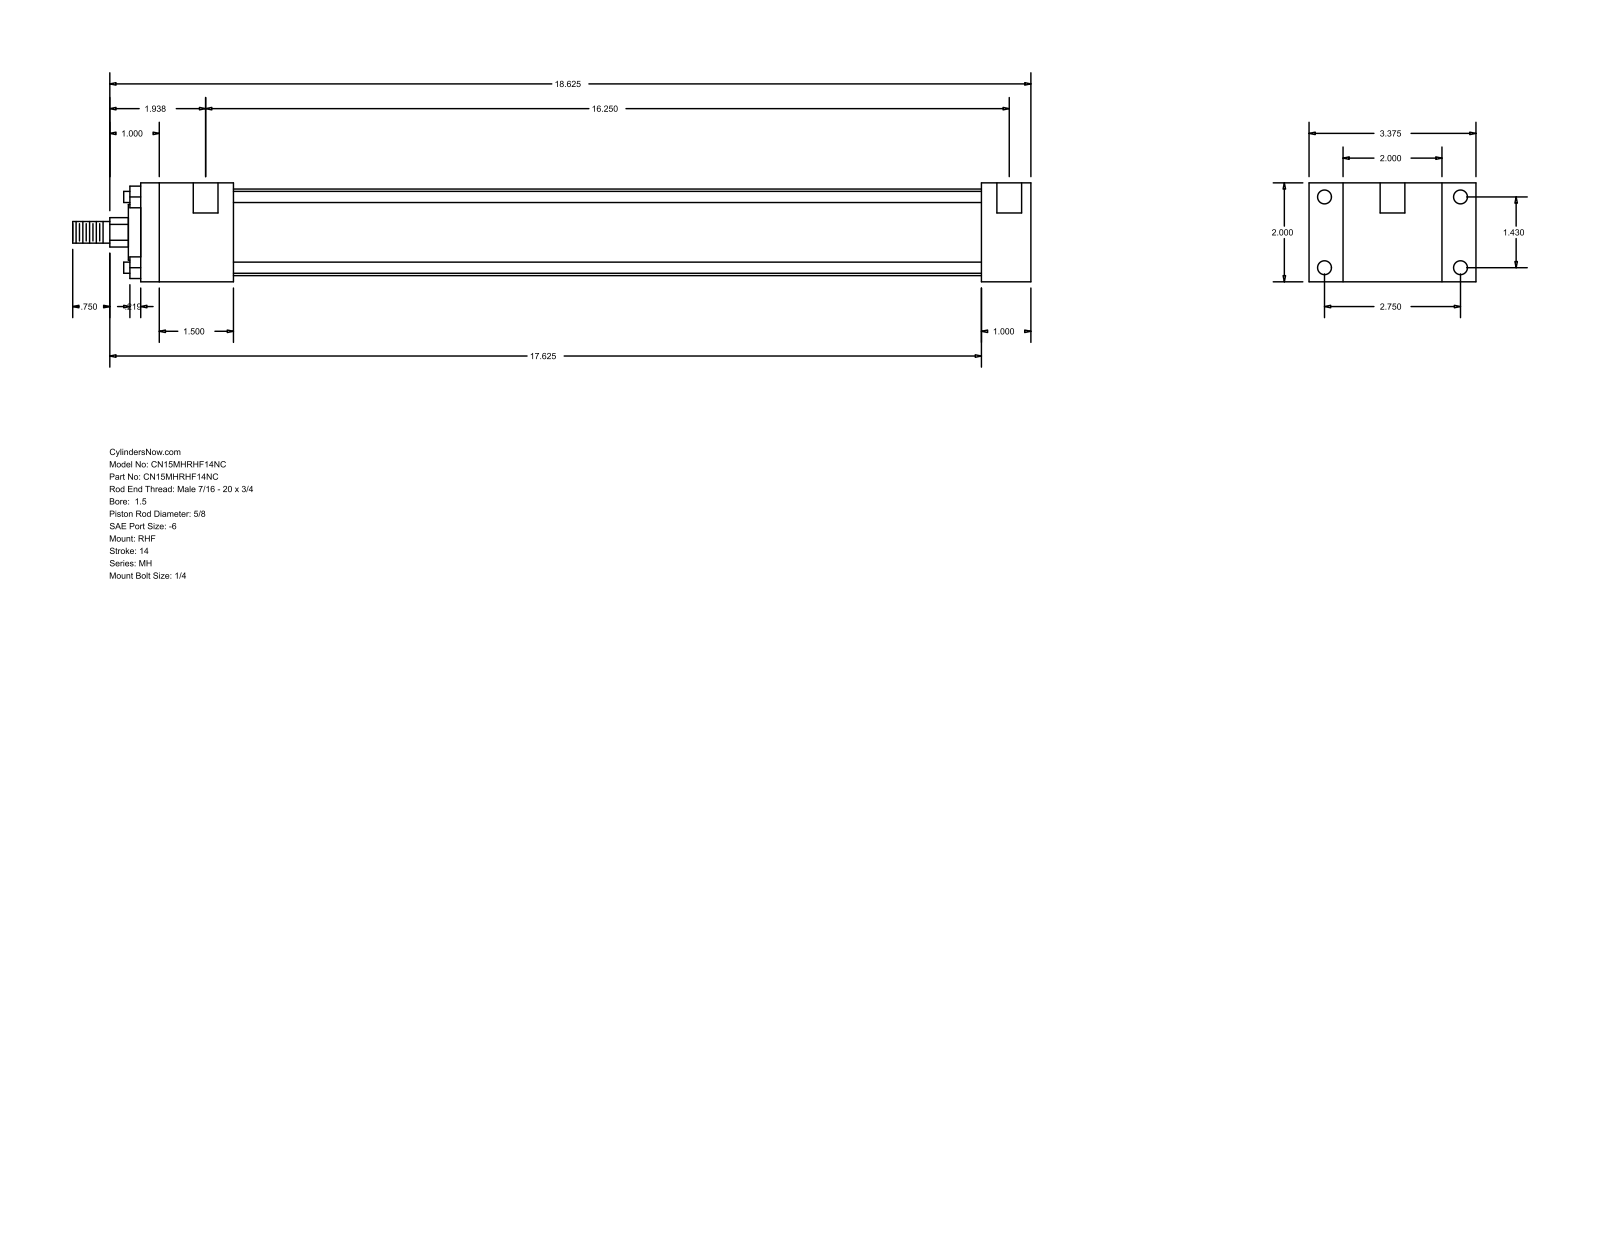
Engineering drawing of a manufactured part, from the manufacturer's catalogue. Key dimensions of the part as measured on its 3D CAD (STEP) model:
Part name (STEP PRODUCT): MH_RHF__0150_0.625
STEP written by: GSSL Pune (CONFIG_CONTROL_DESIGN)
Units: millimetres
Bodies: 0 solids, 88 faces (60 planar, 28 cylindrical, 0 other)
Overall size (bounding box): 492.12 × 85.72 × 50.8
Round holes (diameter × count): ⌀5.56 ×4, ⌀7.14 ×4, ⌀12.7 ×2
Round bosses / shafts (diameter × count): ⌀5.71 ×4, ⌀44.45 ×1, ⌀28.57 ×1, ⌀15.88 ×1, ⌀11.11 ×1
Partial cylindrical surfaces — rounded edges, fillets, slot ends (radius × count): R7.54 ×1
Main face-to-face distances: 50.8, 17.46, 68.26, 25.39, 431.8, 457.19, 85.72, 47.62, 384.18, 409.57
Hole centre spacings: 36.32, 69.84, 78.72, 415.92, 3.17, 412.75
